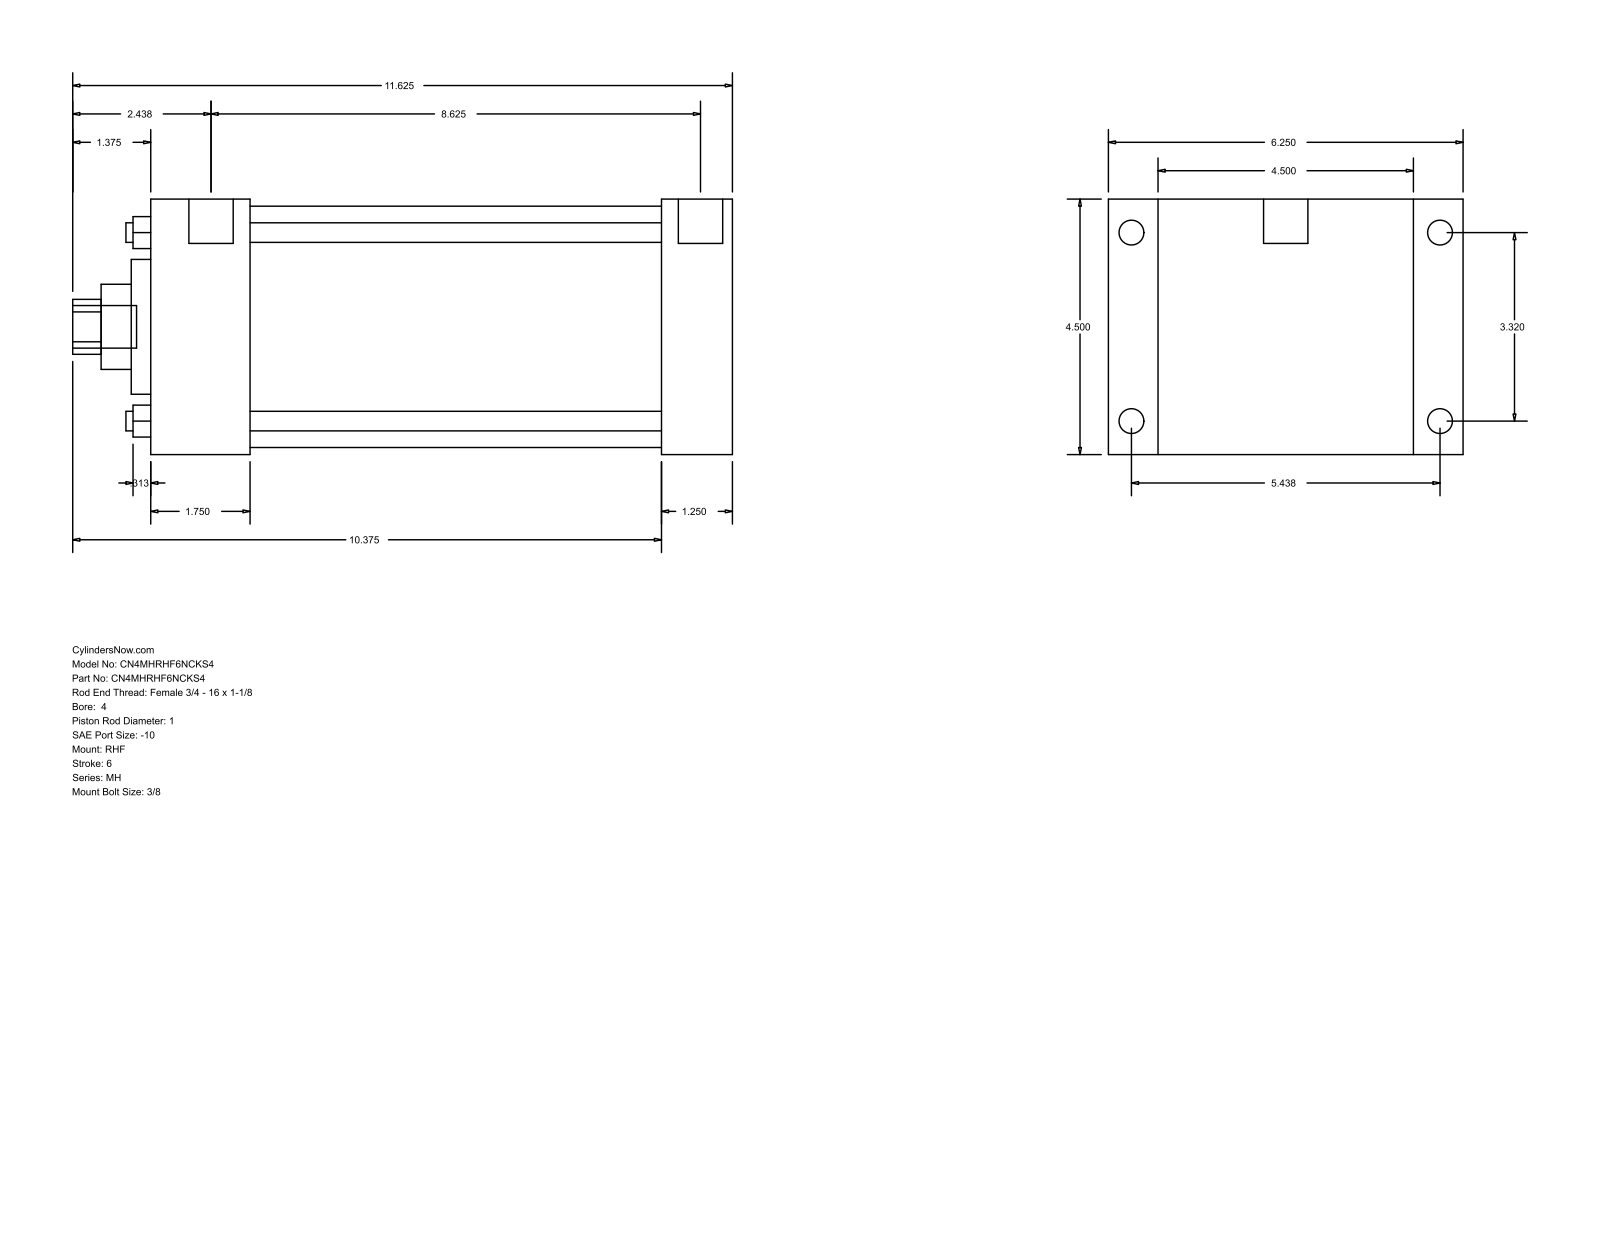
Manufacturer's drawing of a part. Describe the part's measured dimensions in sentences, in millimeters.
The part is named "MH_RHF__0400_1". Its 3-D file was written by "GSSL Pune (CONFIG_CONTROL_DESIGN)". It is 0 solids with 90 faces: 61 planar, 29 cylindrical and 0 other. Overall it measures 295.27 by 158.75 by 114.3 millimeters. Round holes: 4 of diameter 8.76, 1 of diameter 25.4, 1 of diameter 38.1, 1 of diameter 60.33, 1 of diameter 107.95. Round bosses or shafts: 4 of diameter 11.13, 4 of diameter 8.73, 2 of diameter 19.84, 1 of diameter 19.05. Partial cylindrical surfaces (rounded edges, fillets, slot ends): 1 of radius 12.29. The main face-to-face distances are 114.3, 260.35, 228.6, 31.75, 22.23, 136.53, 44.46, 184.14, 215.89, 158.76. The hole center spacings are 59.62, 84.32, 119.25.
